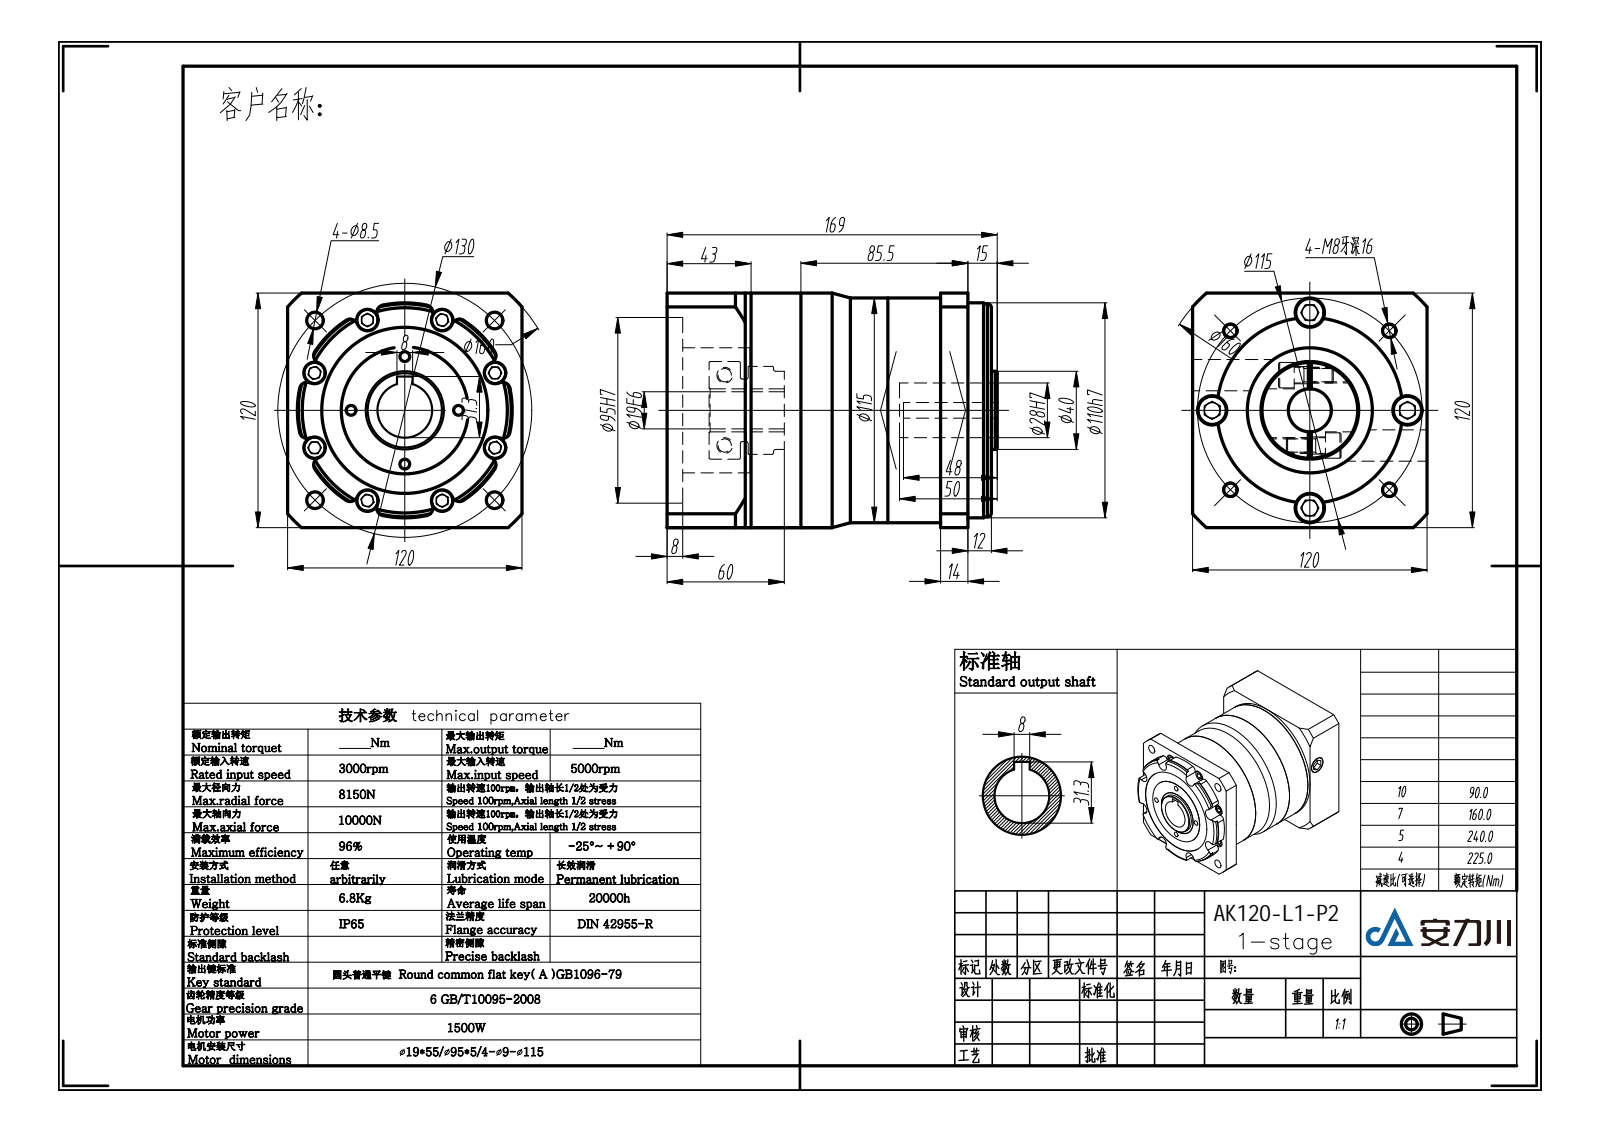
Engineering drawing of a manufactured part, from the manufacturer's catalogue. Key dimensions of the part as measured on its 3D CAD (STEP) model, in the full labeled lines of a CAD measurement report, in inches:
Part name (STEP PRODUCT): VGK115单级模型（19-55 95-5 4-9-115）
STEP written by: SolidWorks 2016 (AUTOMOTIVE_DESIGN)
Units: inches
Bodies: 5 solids, 381 faces (186 planar, 170 cylindrical, 25 other)
Overall size (bounding box): 6.654 × 4.724 × 4.724
Volume: 106.6 in³ · Surface area: 324.6 in²
Round holes (diameter × count): ⌀0.433 ×8, ⌀0.197 ×4, ⌀0.268 ×4, ⌀0.335 ×4, ⌀0.591 ×4, ⌀0.63 ×2, ⌀0.748 ×1, ⌀0.866 ×1, ⌀1.102 ×1, ⌀1.78 ×1, ⌀2.756 ×1, ⌀3.346 ×1
Round bosses / shafts (diameter × count): ⌀0.374 ×8, ⌀0.531 ×4, ⌀0.614 ×2, ⌀4.724 ×1, ⌀4.528 ×1, ⌀2.559 ×1, ⌀1.969 ×1, ⌀1.772 ×1
Partial cylindrical surfaces — rounded edges, fillets, slot ends (radius × count): R0.157 ×16, R2.146 ×1, R2.165 ×1, R3.15 ×1
Main face-to-face distances: 1.004, 2.756, 1.752, 4.724, 3.839, 4.449, 1.024, 1.693, 2.697, 4.37
Hole centre spacings: 0.768, 0.875, 1.053, 1.056, 1.643, 1.683, 1.817, 1.848
